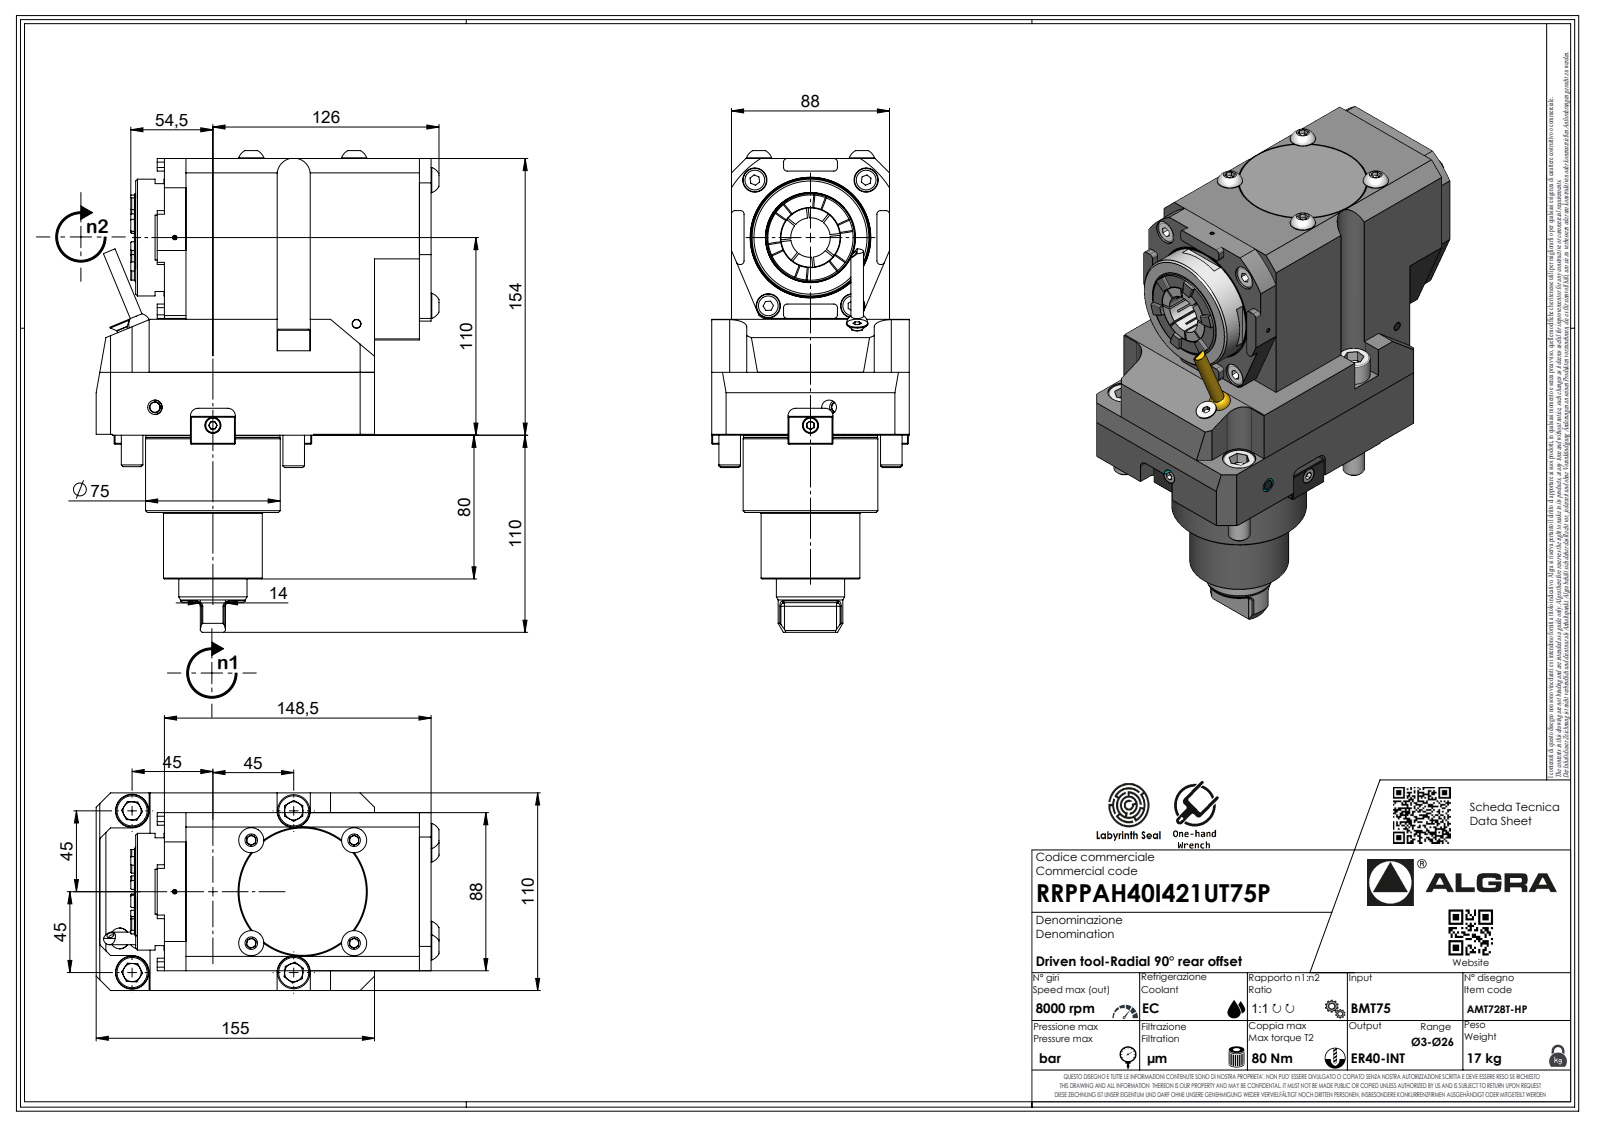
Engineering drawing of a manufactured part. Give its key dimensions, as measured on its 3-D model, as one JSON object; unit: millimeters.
{"part_name": "RRPPAH40I421UT75P", "step_written_by": "SolidWorks 2023 (AUTOMOTIVE_DESIGN)", "units": "millimeters", "bodies": {"solids": 1, "faces": 694, "planar": 477, "cylindrical": 110, "other": 107}, "overall_size": [263.7, 186.5, 110], "volume_mm3": 2512000, "surface_area_mm2": 149039, "round_holes": [[2.1, 1], [4, 1]], "round_bosses_or_shafts": [[12, 4], [18, 2], [75, 1], [74.6, 1], [65, 1], [55, 1], [38, 1], [36, 1]], "partial_cylinders_radius": [[2, 23], [0.33, 7], [0.52, 7], [3.7, 7], [50.03, 6], [4.25, 4], [1, 2], [9.25, 2]], "face_to_face_distances": [11, 99, 88, 110, 154, 31.5, 0.5, 64.5, 38, 64]}
